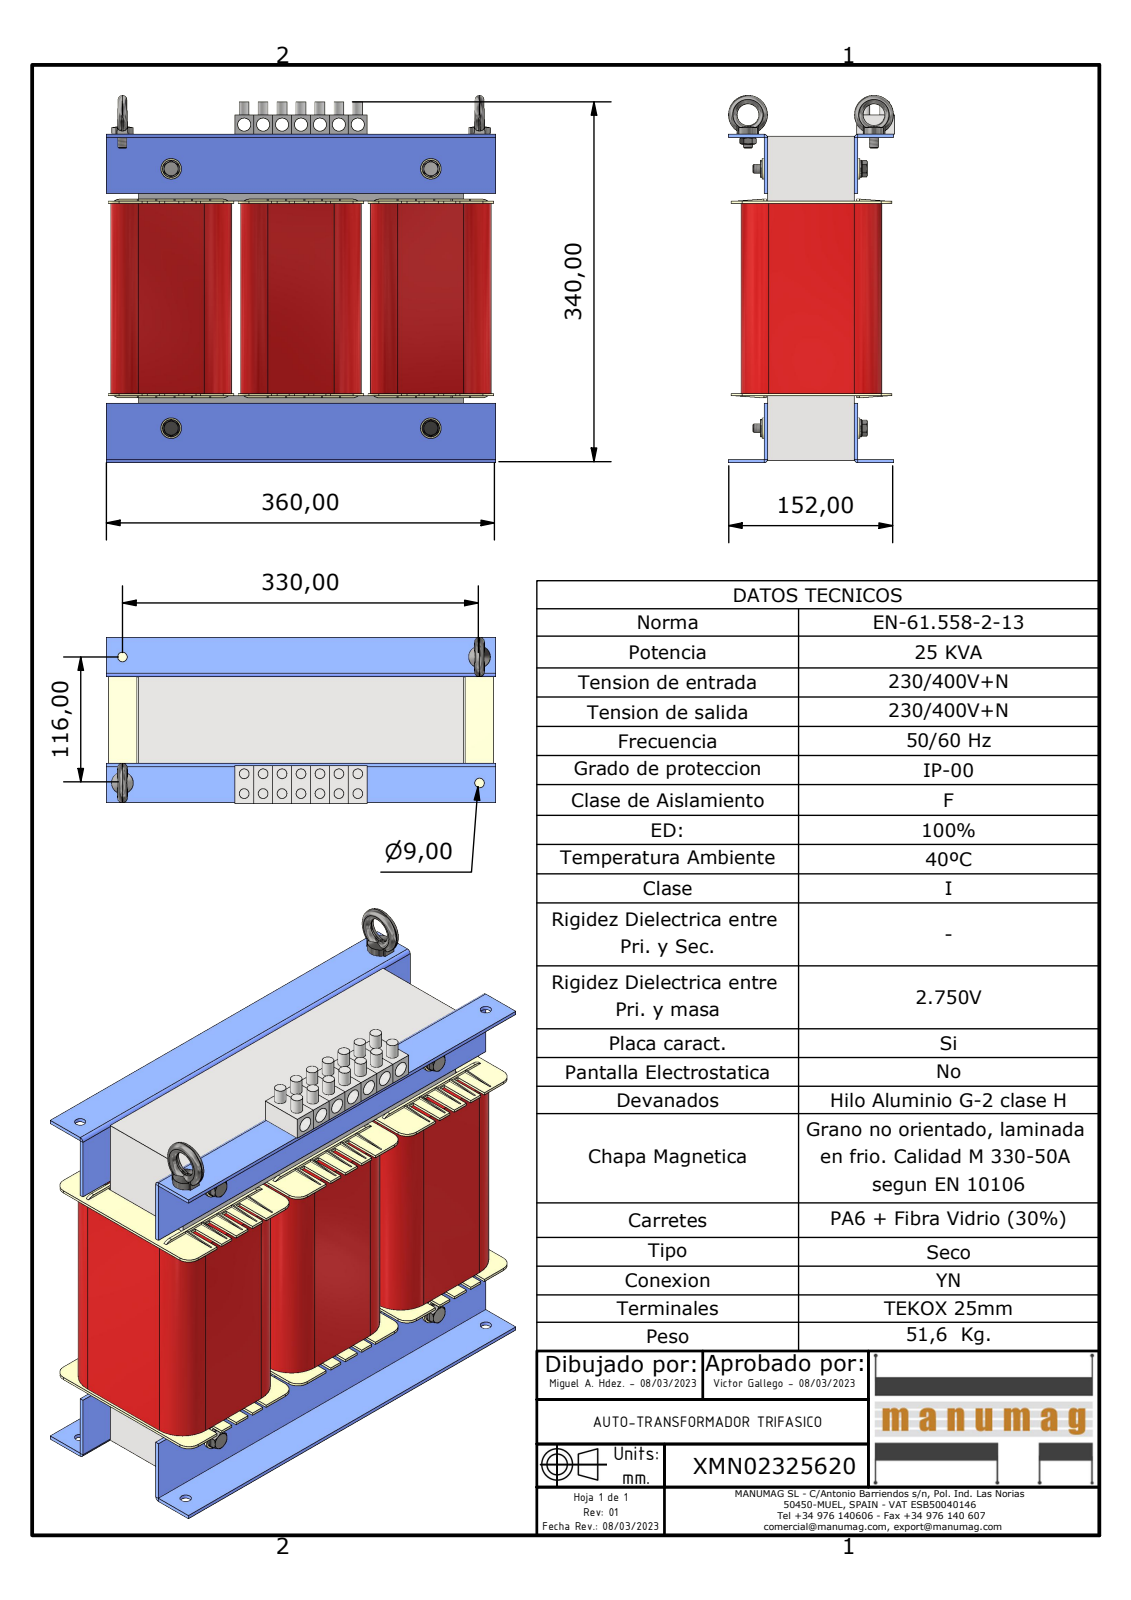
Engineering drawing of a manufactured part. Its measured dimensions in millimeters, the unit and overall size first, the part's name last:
Units: millimetres
Overall size (bounding box): 360 × 340 × 153
Round holes (diameter × count): ⌀12 ×7, ⌀8 ×4, ⌀8.4 ×4, ⌀9 ×4, ⌀10.5 ×4, ⌀11 ×4, ⌀20 ×2, ⌀6.65 ×1
Round bosses / shafts (diameter × count): ⌀9 ×14, ⌀19 ×4, ⌀16 ×4, ⌀11.4 ×4, ⌀9.6 ×4, ⌀7.32 ×4, ⌀36 ×2, ⌀8 ×2
Partial cylindrical surfaces — rounded edges, fillets, slot ends (radius × count): R10 ×26, R1 ×14, R2 ×12, R3 ×12, R3.31 ×12, R25.37 ×12, R9 ×6, R3 ×4
Main face-to-face distances: 1, 2, 3, 120, 83, 60, 22.37, 23.37, 80, 240
Hole centre spacings: 17.5, 35, 52.5, 240, 70, 116, 78.91, 87.5
Volume: 10 520 000 mm³ · Surface area: 1 466 000 mm²
Bodies: 38 solids, 1250 faces (918 planar, 260 cylindrical, 72 other)
Part name (STEP PRODUCT): XMN02325620; UI 180 - 80 (300x300); UI 180_80_BOBINADO; RC60 NT060 (+7 more)
STEP written by: Autodesk Inventor 2023 (AUTOMOTIVE_DESIGN)
